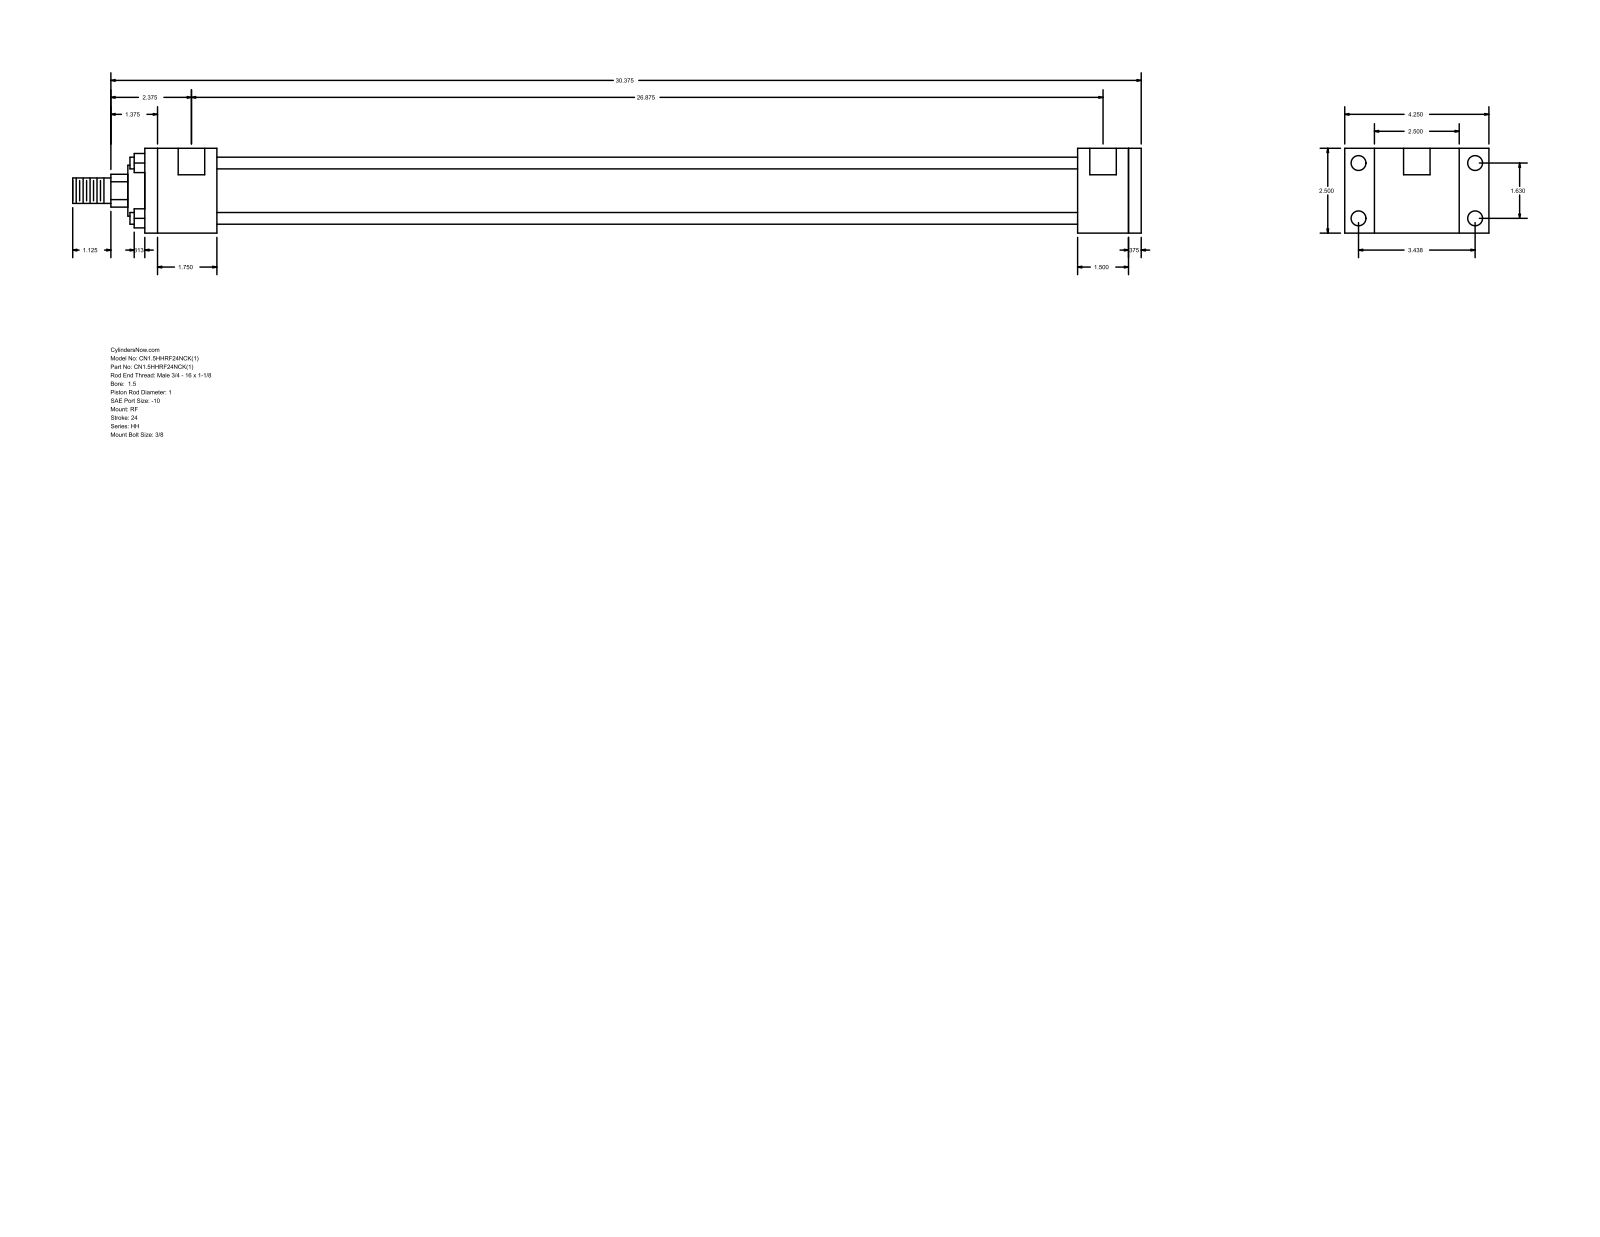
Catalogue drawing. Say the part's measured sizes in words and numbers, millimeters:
The part is named "HH_RF__0150_1". Its 3-D file was written by "GSSL Pune (CONFIG_CONTROL_DESIGN)". It is 0 solids with 92 faces: 64 planar, 28 cylindrical and 0 other. Overall it measures 800.1 by 107.95 by 63.5 millimeters. Round holes: 4 of diameter 5.56, 4 of diameter 11.13, 2 of diameter 19.84. Round bosses or shafts: 4 of diameter 8.76, 1 of diameter 44.45, 1 of diameter 38.1, 1 of diameter 25.4, 1 of diameter 19.05. Partial cylindrical surfaces (rounded edges, fillets, slot ends): 1 of radius 12.29. The main face-to-face distances are 63.5, 9.52, 38.1, 644.52, 682.62, 692.14, 47.62, 53.98, 698.5, 736.6. The hole center spacings are 1.59, 41.4, 87.32, 96.64, 684.21, 685.8, 682.62.
